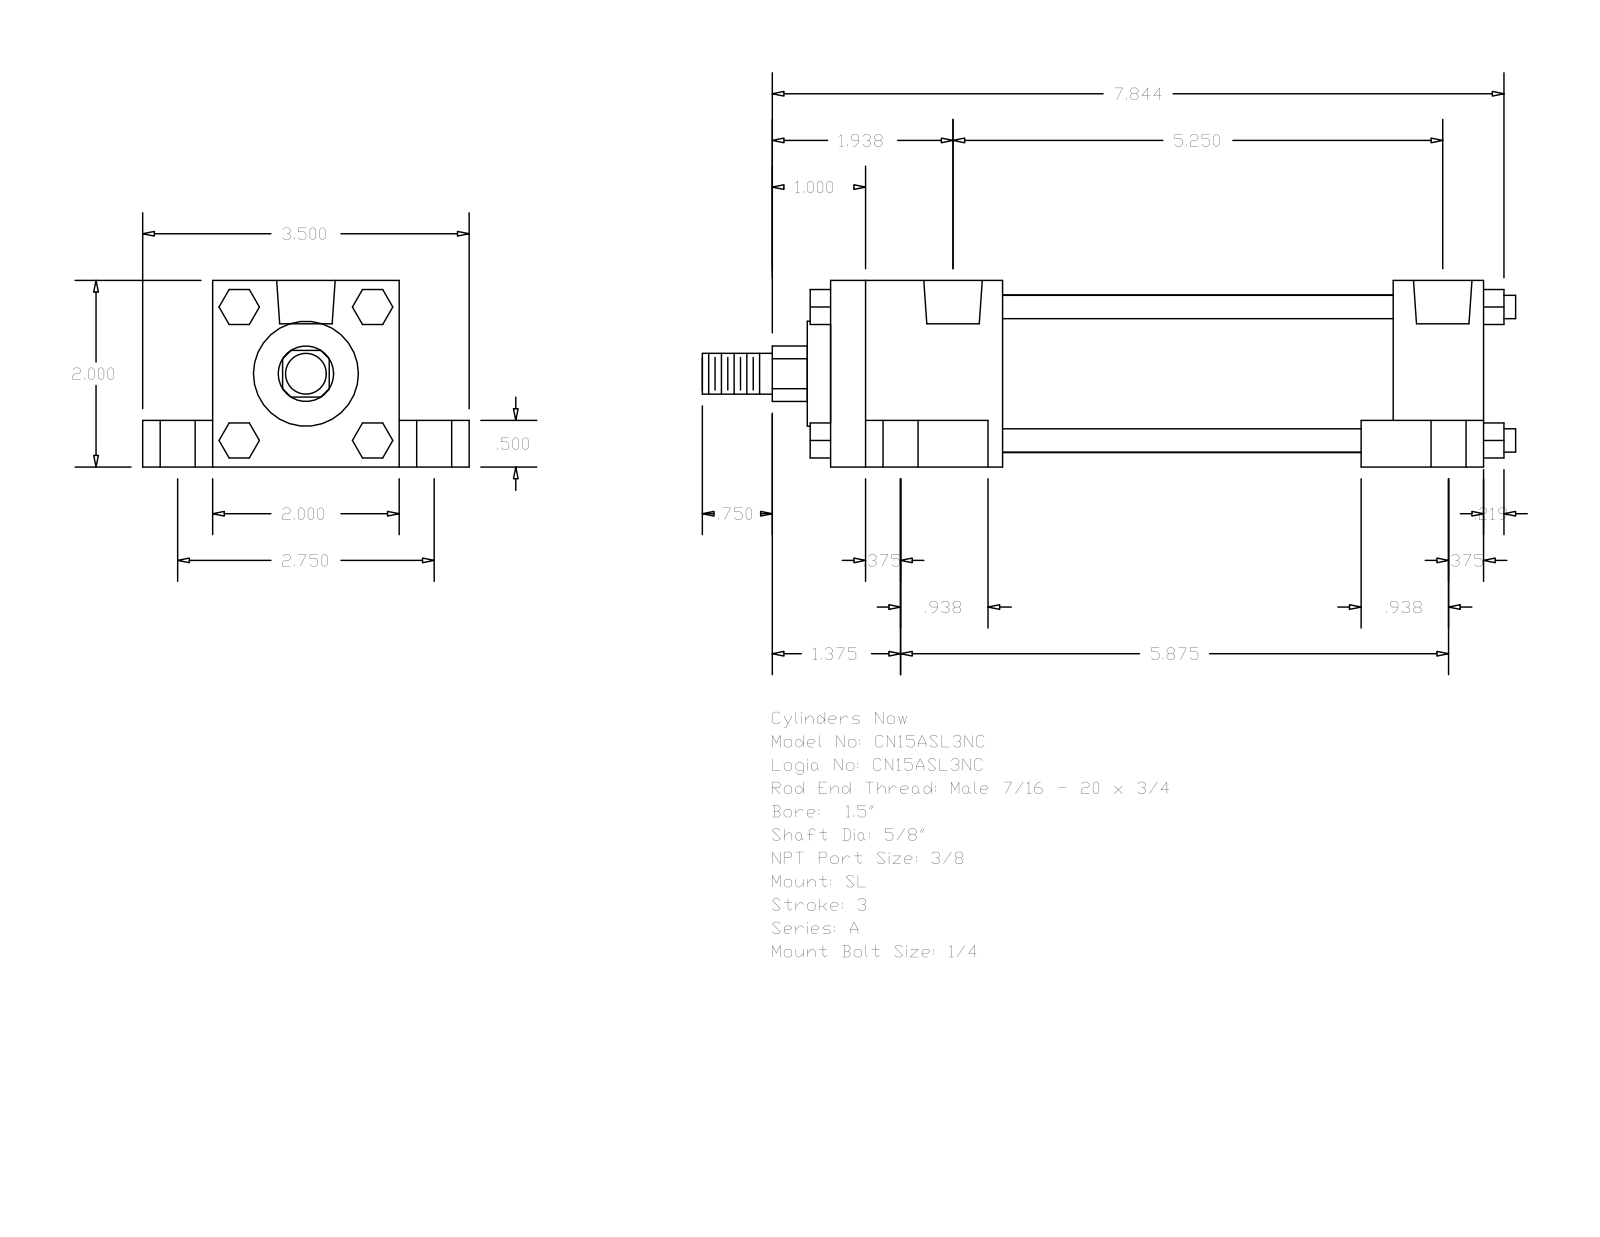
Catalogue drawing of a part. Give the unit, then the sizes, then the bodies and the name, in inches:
Units: inches
Overall size (bounding box): 8.719 × 3.5 × 2
Round holes (diameter × count): ⌀0.219 ×4, ⌀0.375 ×4, ⌀0.625 ×4, ⌀0.627 ×2
Round bosses / shafts (diameter × count): ⌀0.25 ×4, ⌀1.69 ×1, ⌀1.125 ×1, ⌀0.625 ×1, ⌀0.437 ×1
Partial cylindrical surfaces — rounded edges, fillets, slot ends (radius × count): R0.297 ×1
Main face-to-face distances: 2, 0.75, 1.5, 0.5, 2.75, 7, 0.375, 1.313, 6.031, 0.969
Hole centre spacings: 0.156, 1.376, 1.392, 1.485, 1.552, 2.75, 4.937, 5.094
Bodies: 0 solids, 148 faces (112 planar, 36 cylindrical, 0 other)
Part name (STEP PRODUCT): A_SL__0150_0.625
STEP written by: GSSL Pune (CONFIG_CONTROL_DESIGN)
